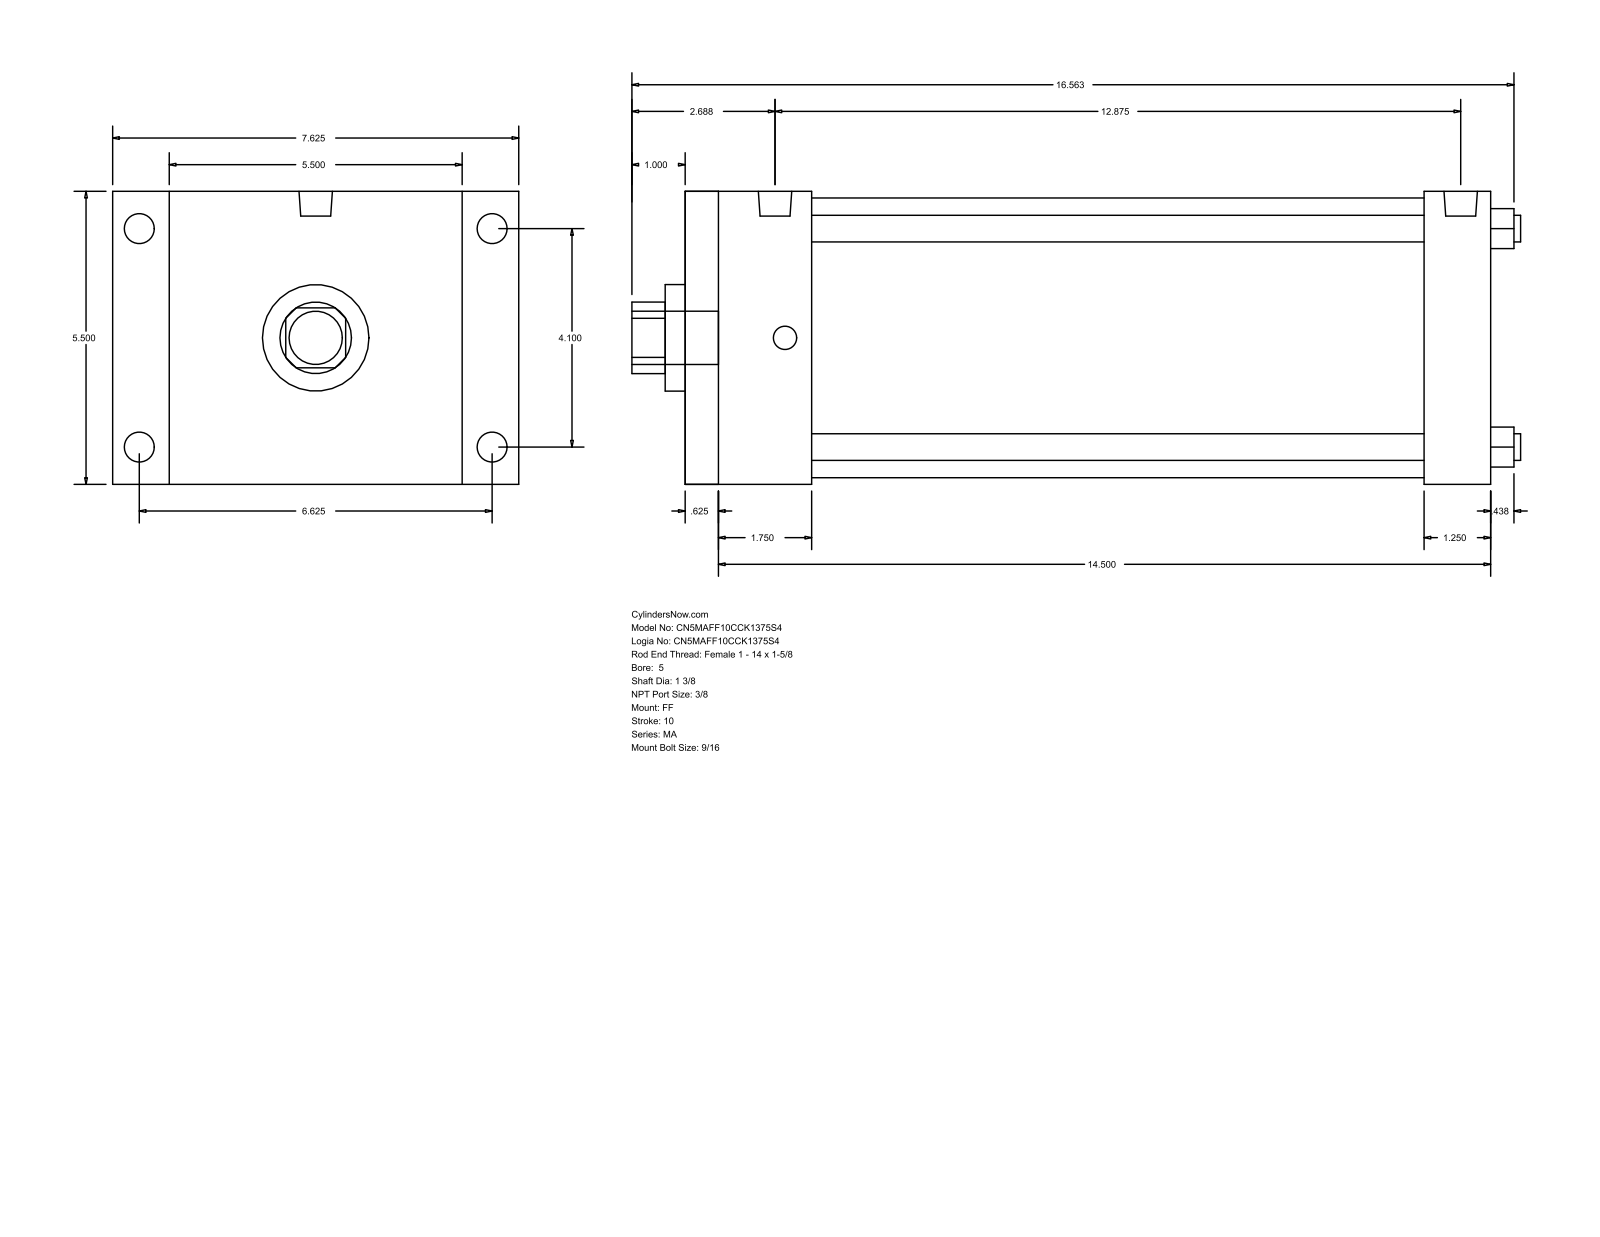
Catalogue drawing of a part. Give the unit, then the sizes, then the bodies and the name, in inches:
Units: inches
Overall size (bounding box): 16.687 × 7.625 × 5.5
Round holes (diameter × count): ⌀0.5 ×4, ⌀1.375 ×1, ⌀2 ×1, ⌀5.25 ×1
Round bosses / shafts (diameter × count): ⌀0.563 ×4, ⌀0.437 ×4, ⌀0.627 ×2, ⌀1 ×1
Partial cylindrical surfaces — rounded edges, fillets, slot ends (radius × count): R0.672 ×1
Main face-to-face distances: 5.5, 15.125, 0.625, 14.5, 13.875, 13.25, 1.25, 2.375, 1.75, 11.5
Hole centre spacings: 2.899, 4.1, 5.798
Bodies: 0 solids, 92 faces (64 planar, 28 cylindrical, 0 other)
Part name (STEP PRODUCT): MA_FF__0500_1.375
STEP written by: GSSL Pune (CONFIG_CONTROL_DESIGN)
